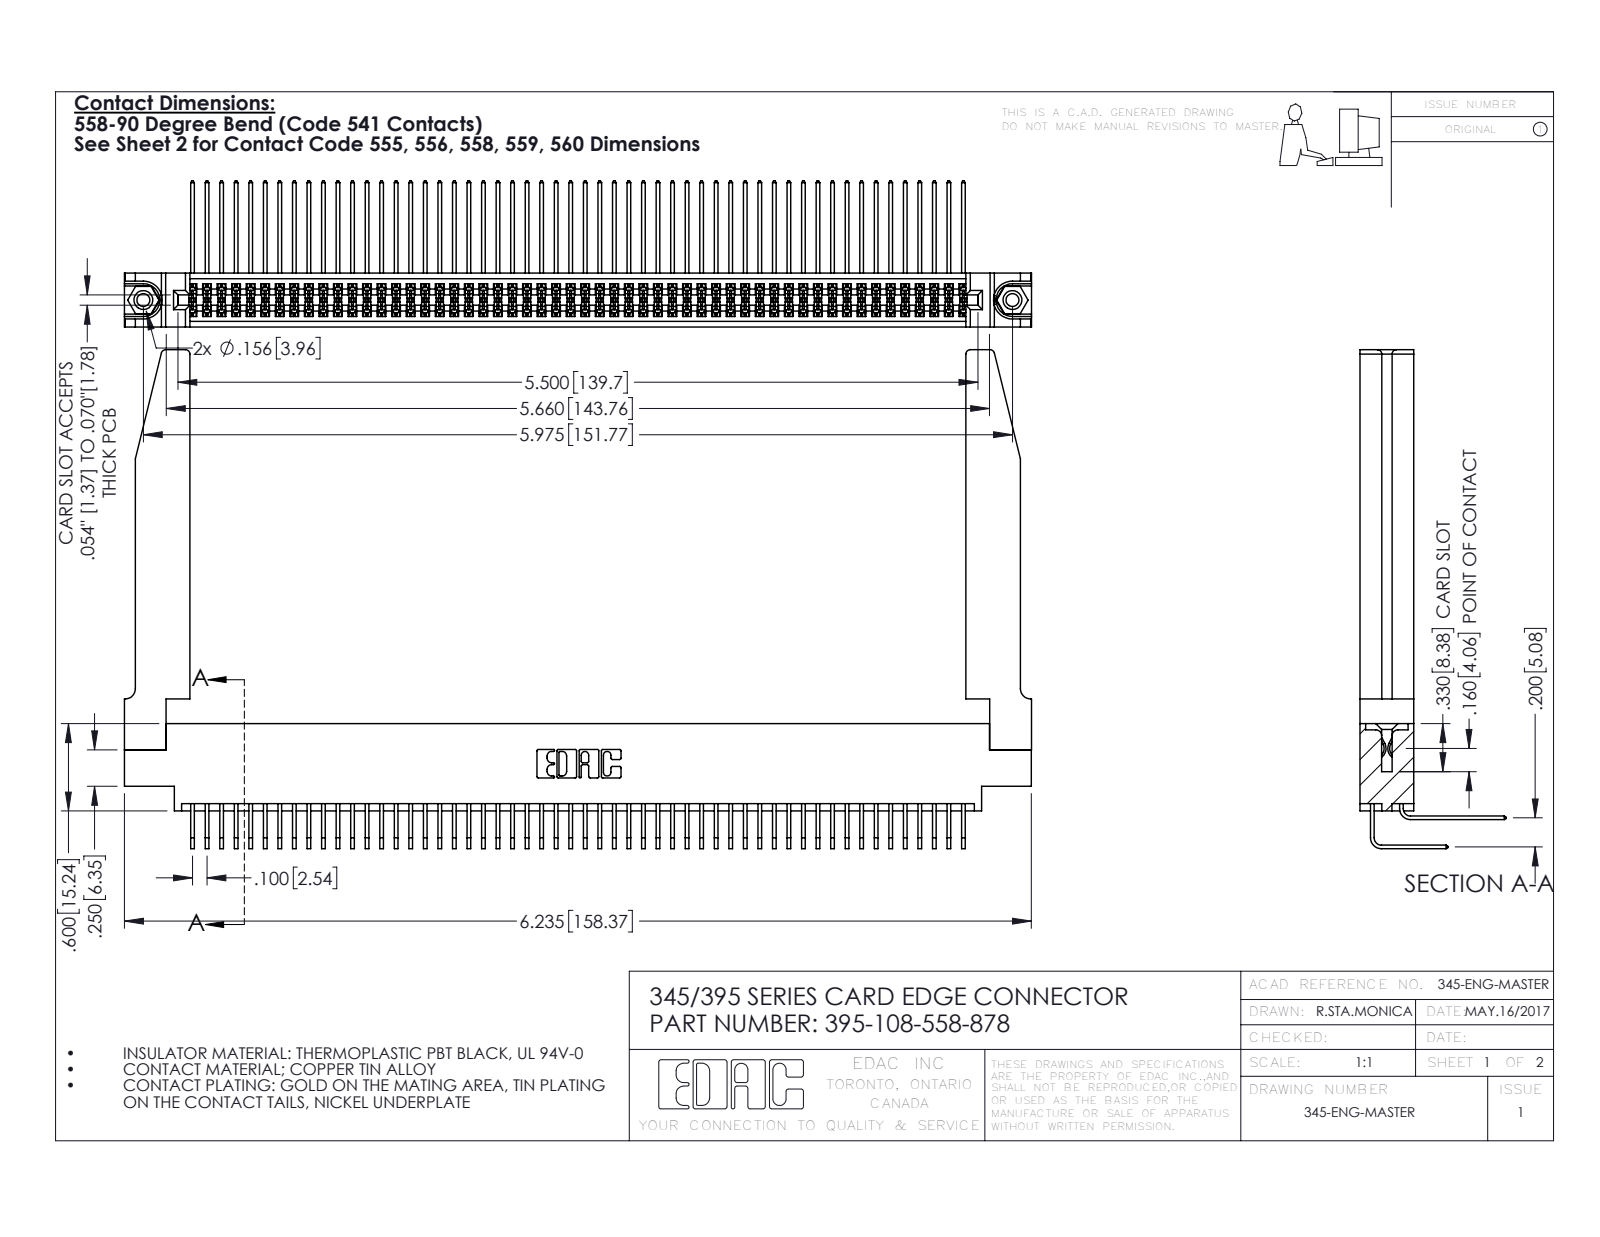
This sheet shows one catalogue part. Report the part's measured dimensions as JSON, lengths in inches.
{"part_name": "345 Part_0.170 Offset - 0.156 Dia-TH; 345-292-001_558 559 Tail - 1; 345-292-001_558 Tail - 2; 395-108-558-878 (+2 more)", "step_written_by": "SolidWorks 2016 (CONFIG_CONTROL_DESIGN)", "units": "inches", "bodies": {"solids": 113, "faces": 5980, "planar": 4006, "cylindrical": 1922, "other": 52}, "overall_size": [6.236, 3.429, 1.005], "volume_in3": 1.451, "surface_area_in2": 52.4, "round_holes": [[0.089, 2], [0.125, 2], [0.156, 2], [0.064, 1]], "round_bosses_or_shafts": [[0.155, 2]], "partial_cylinders_radius": [[0.006, 162], [0.01, 22], [0.03, 8], [0.007, 6], [0.031, 6], [0.026, 3], [0.014, 2], [0.019, 2]], "face_to_face_distances": [0.072, 0.37, 0.298, 0.2, 0.098, 0.272, 0.025, 0.225, 0.175, 0.025], "hole_center_spacings": [0.27, 5.739, 5.975]}
